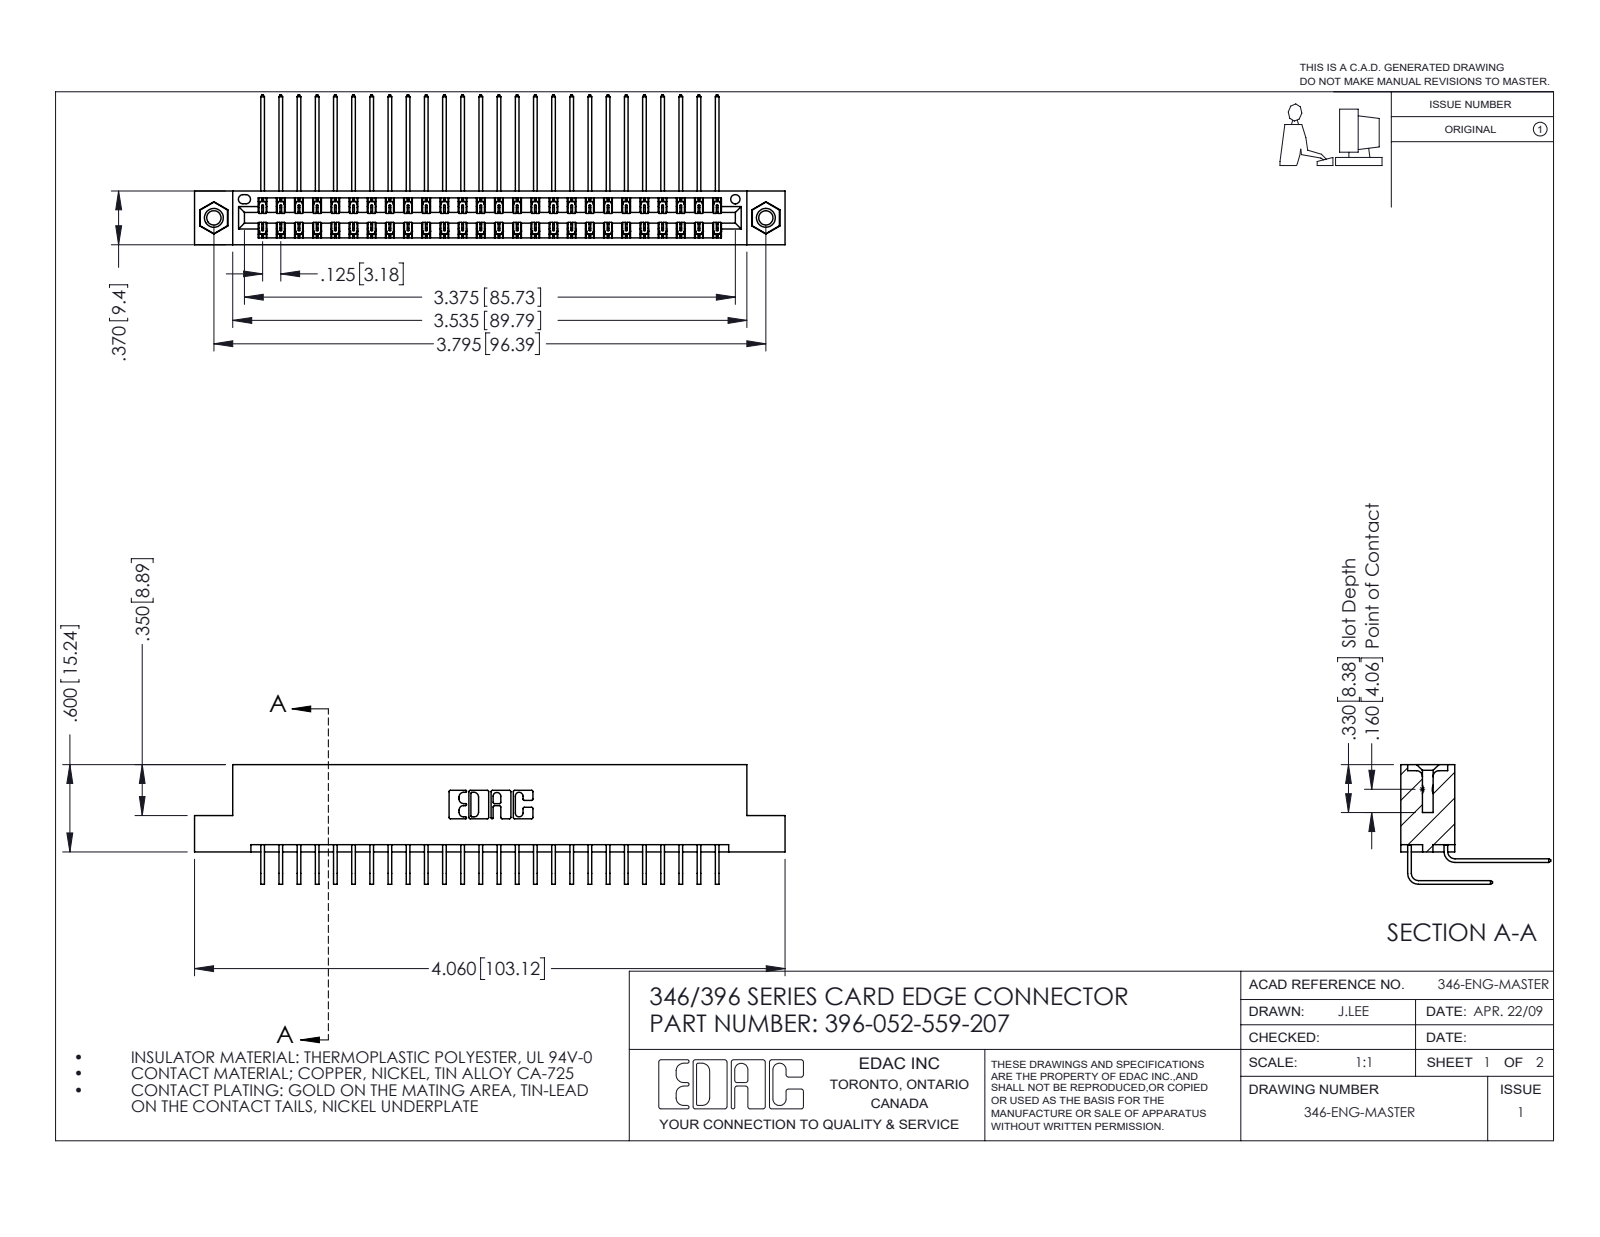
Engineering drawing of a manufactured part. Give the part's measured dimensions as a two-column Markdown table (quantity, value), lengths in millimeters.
| quantity | value |
| --- | --- |
| part name | 346 Part_Flush Mounting Lugs - 0.156 Dia-TI; 396-052-559-207; 345-292-001_558 559 Tail - 1; 345-292-001_559 Tail - 2 (+1 more) |
| STEP written by | SolidWorks 2016 (CONFIG_CONTROL_DESIGN) |
| units | millimeters |
| bodies | 55 solids, 2990 faces (2032 planar, 942 cylindrical, 16 other) |
| overall size | 103.1 × 26.2 × 20.9 |
| volume | 10 200 mm³ |
| surface area | 15 260 mm² |
| round holes (diameter × count) | 2.5 × 2, 3.2 × 2, 4 × 2, 1.6 × 1 |
| round bosses / shafts (diameter × count) | 3.9 × 2 |
| partial cylindrical surfaces (radius × count) | 0.2 × 78, 0.3 × 22, 0.2 × 6, 0.8 × 6, 0.7 × 3, 0.4 × 2, 0.6 × 2, 0.6 × 2 |
| main face-to-face distances | 1.2, 8.2, 0.6, 6.4, 9.4, 1.8, 7.6, 7, 3.8, 5.6 |
| hole center spacings | 6.2, 91.1, 96.4 |
